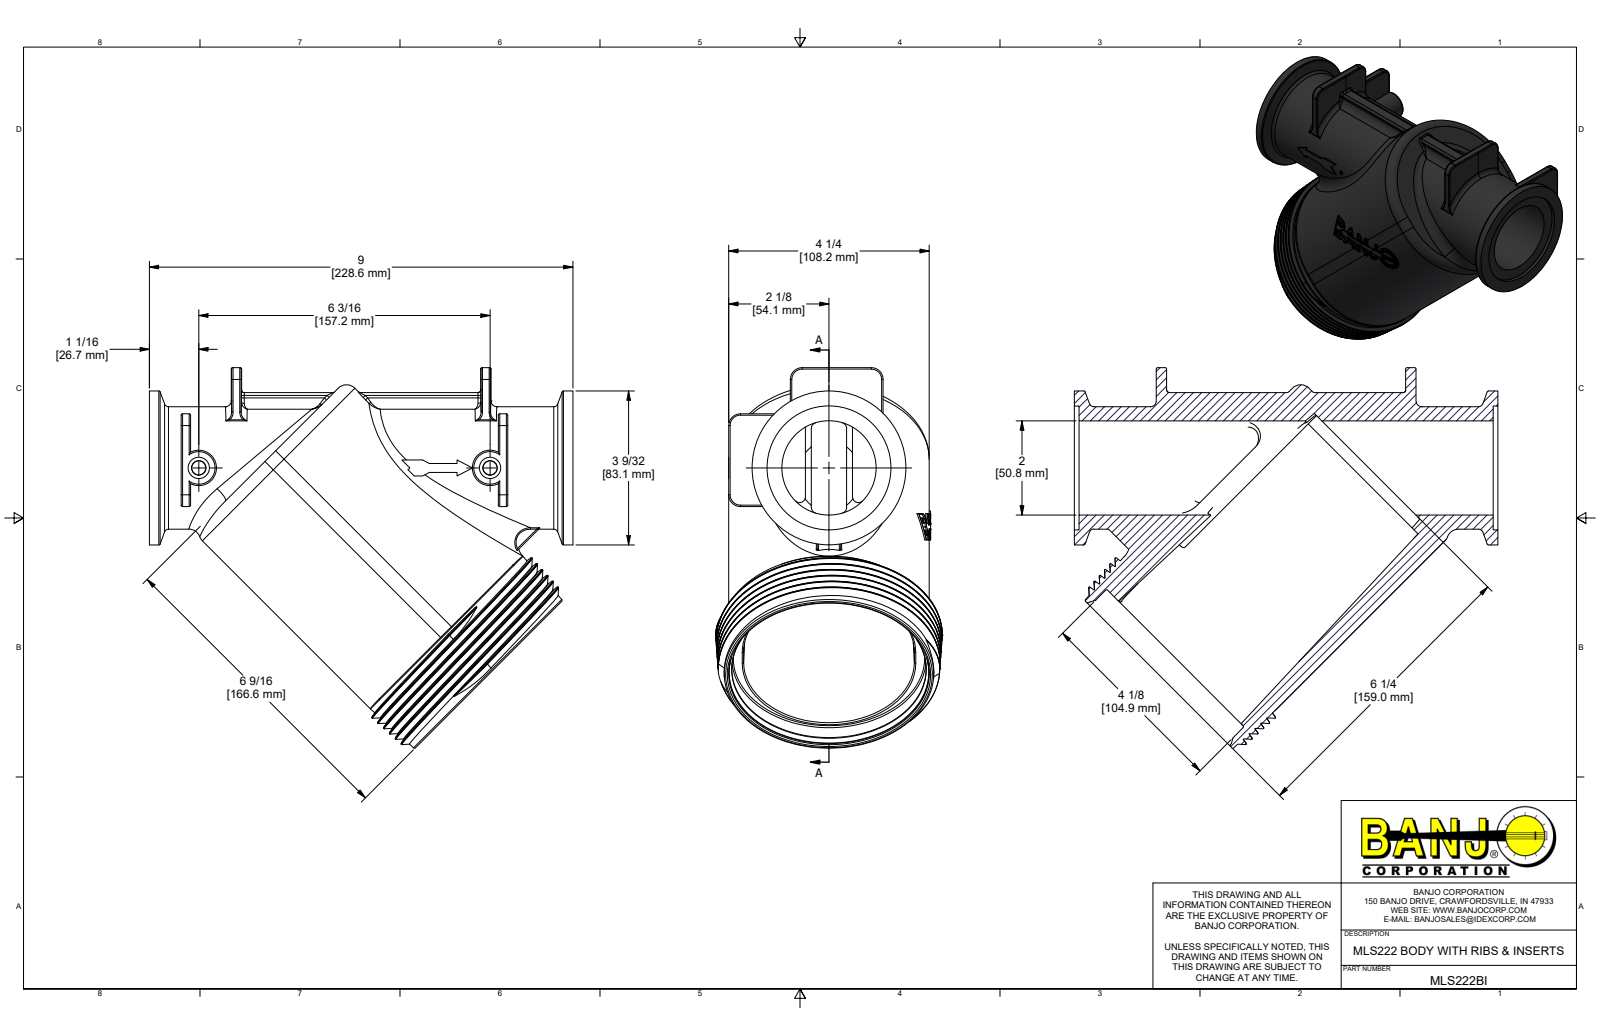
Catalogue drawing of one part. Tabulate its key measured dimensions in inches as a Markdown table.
| quantity | value |
| --- | --- |
| part name | MLS222BI; MLS222B; V25022 |
| STEP written by | Autodesk Inventor 2022 (AUTOMOTIVE_DESIGN) |
| units | inches |
| bodies | 3 solids, 670 faces (295 planar, 180 cylindrical, 195 other) |
| overall size | 9 × 8.081 × 4.815 |
| volume | 51.75 in³ |
| surface area | 314.3 in² |
| round holes (diameter × count) | 0.295 × 2, 0.307 × 2, 0.454 × 1, 0.641 × 1, 2 × 1, 2.63 × 1, 4.13 × 1 |
| round bosses / shafts (diameter × count) | 0.5 × 2, 0.455 × 2, 3.27 × 1, 2.6 × 1, 0.675 × 1 |
| partial cylindrical surfaces (radius × count) | 0.03 × 40, 0.06 × 12, 0.25 × 8, 0.125 × 6, 0.02 × 2, 0.039 × 2, 0.056 × 2, 0.1 × 2 |
| main face-to-face distances | 0.1, 8.9, 0.3, 9, 5.3, 0.2, 6.74, 8.8, 1.755, 2.505 |
| hole center spacings | 2.522, 4.191, 6.19 |
